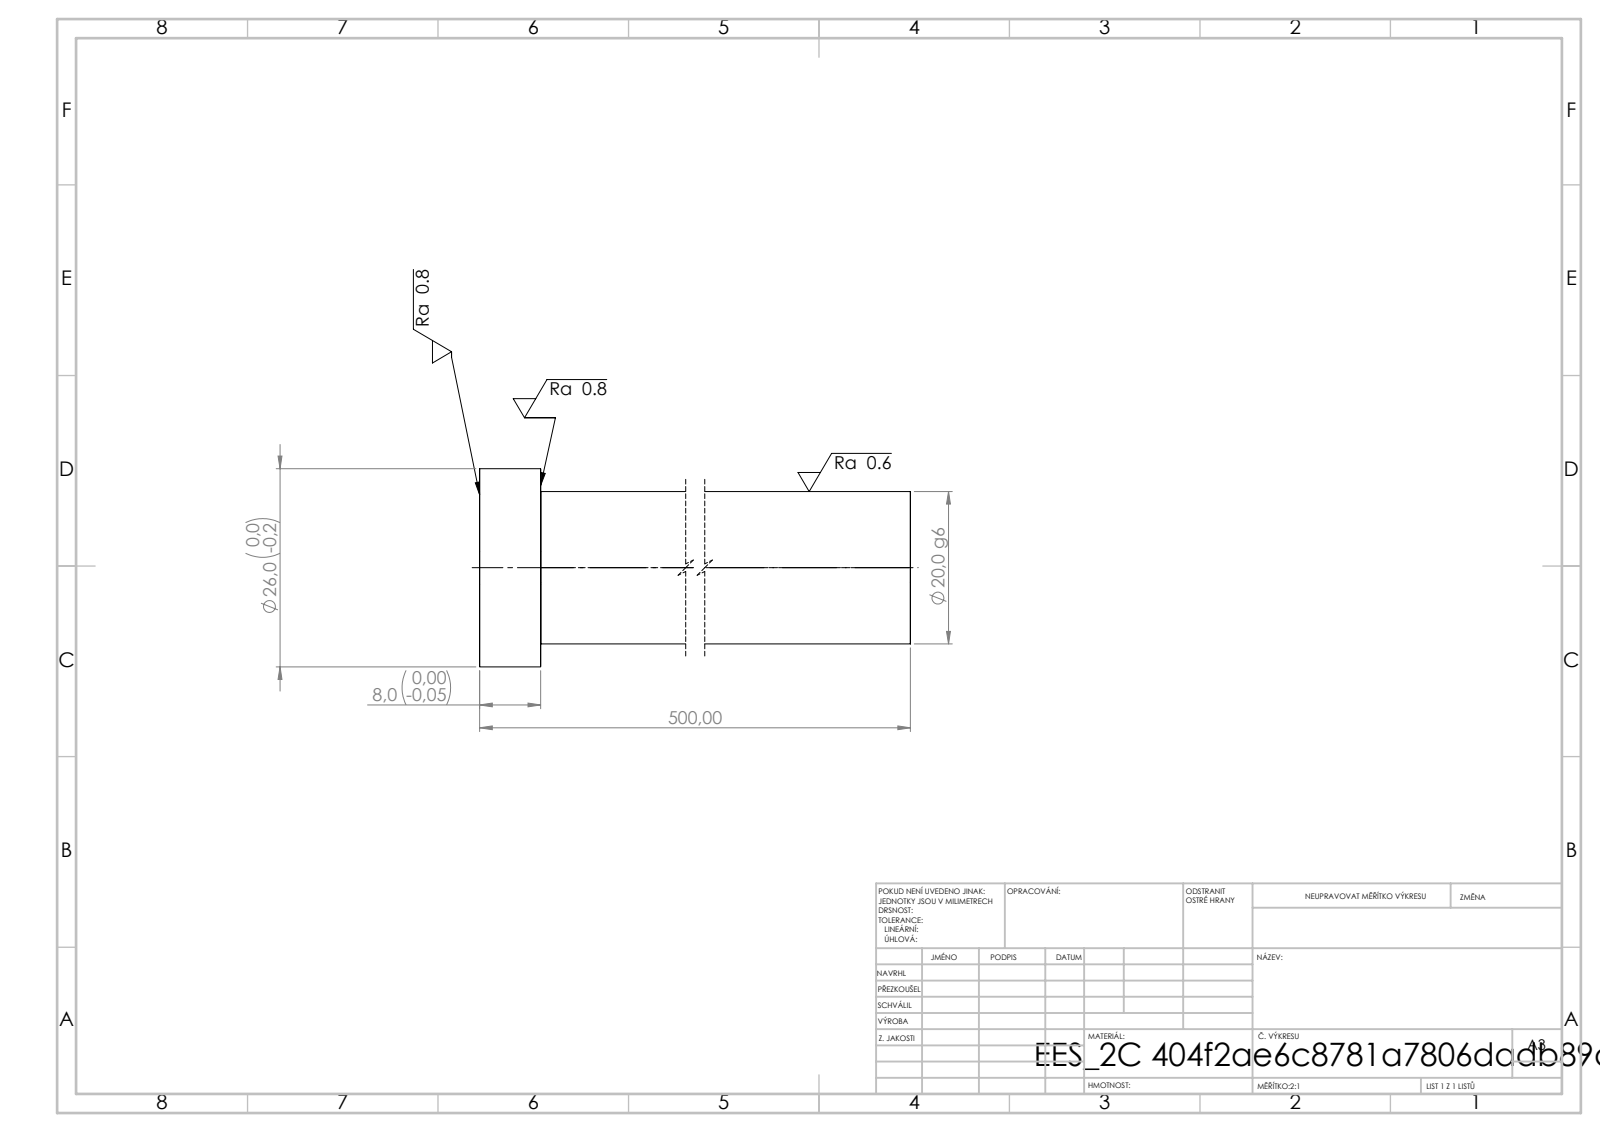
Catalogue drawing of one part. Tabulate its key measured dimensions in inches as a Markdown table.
| quantity | value |
| --- | --- |
| STEP written by | SolidWorks 2019 (CONFIG_CONTROL_DESIGN) |
| units | inches |
| bodies | 1 solid, 7 faces (3 planar, 4 cylindrical, 0 other) |
| overall size | 19.685 × 1.024 × 1.024 |
| volume | 9.691 in³ |
| surface area | 50.58 in² |
| round bosses / shafts (diameter × count) | 1.024 × 1, 0.787 × 1 |
| main face-to-face distances | 19.685, 0.315, 19.37 |
